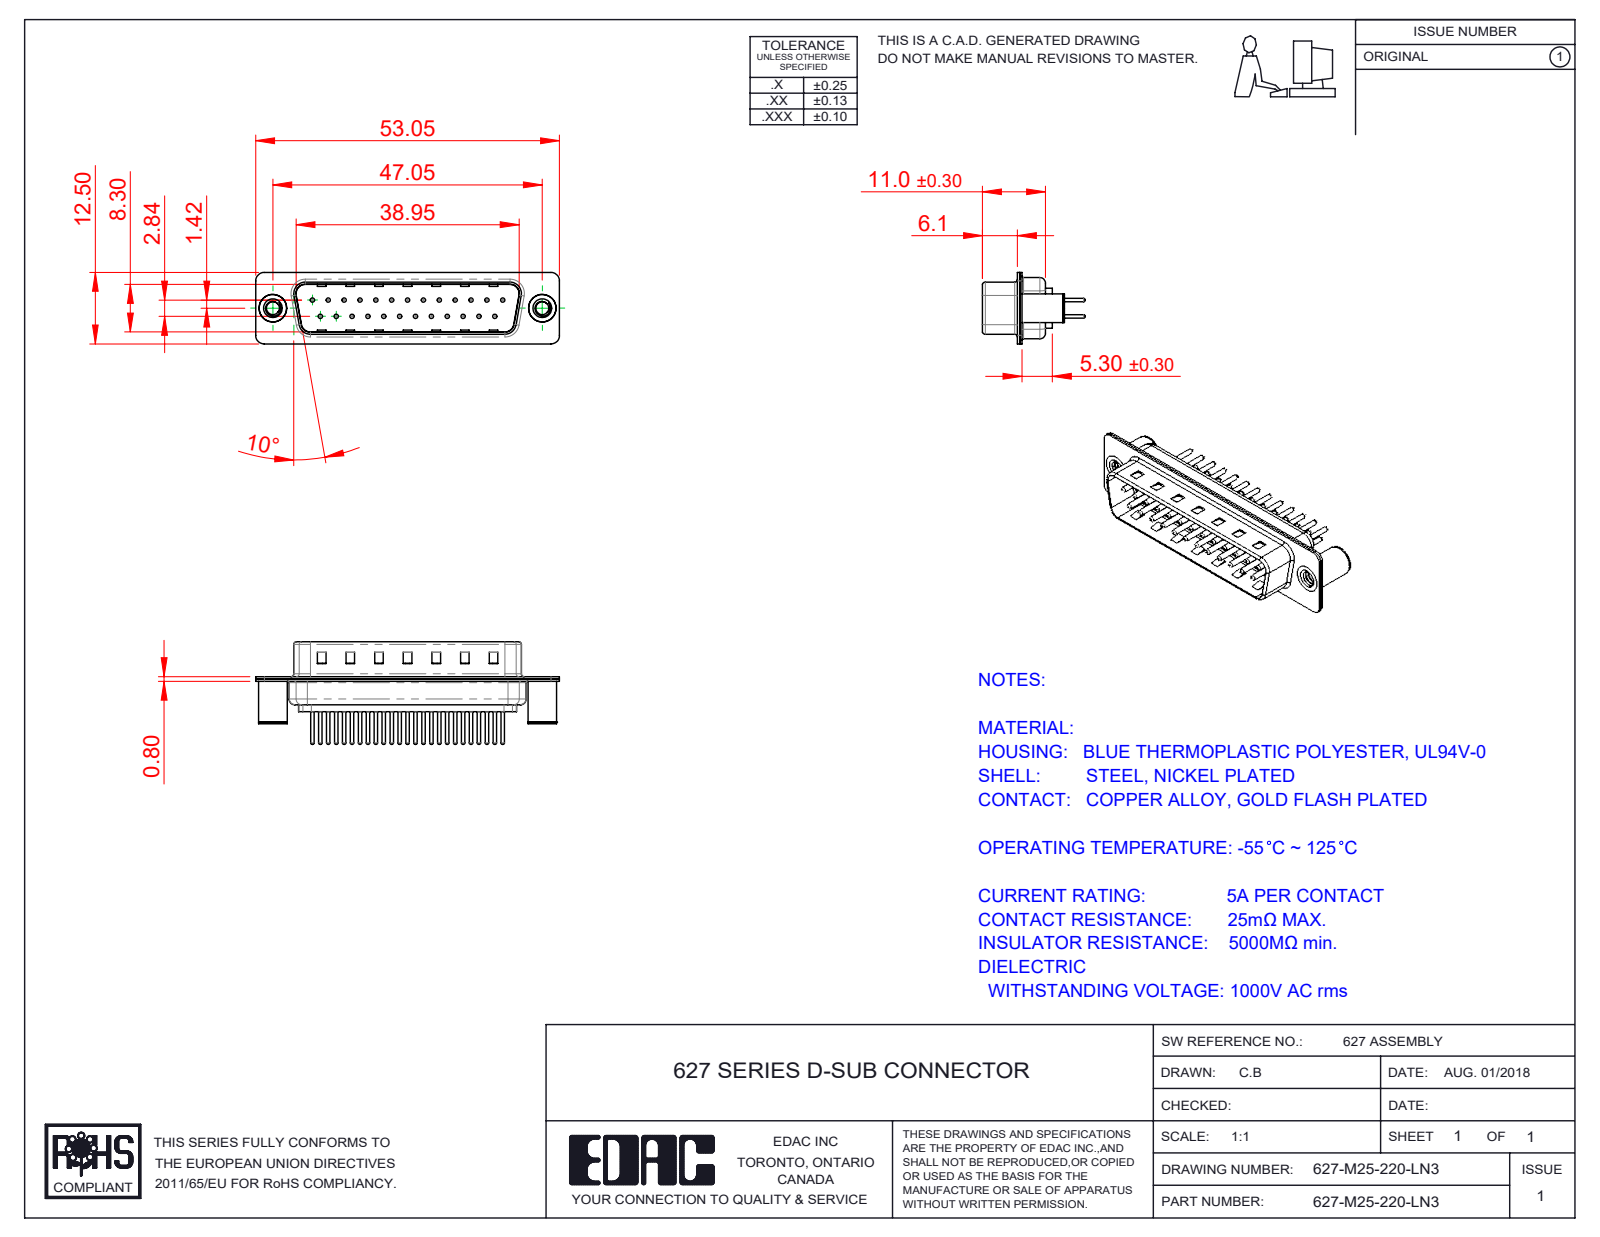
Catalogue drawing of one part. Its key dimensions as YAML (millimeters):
part_name: "627M 4-40 Threaded Board Spacer; 627M Shell Rear_25 Contacts; 627M Contact Row 2_20; 627M Shell Front_25 Contacts (+3 more)"
step_written_by: "SolidWorks 2020 (CONFIG_CONTROL_DESIGN)"
units: millimeters
bodies: {solids: 30, faces: 1335, planar: 346, cylindrical: 511, other: 478}
overall_size: [53.05, 17.9, 12.5]
volume: 2842
surface_area: 7101
round_holes:
  - {diameter: 0.75, count: 25}
  - {diameter: 1.6, count: 25}
  - {diameter: 2, count: 25}
  - {diameter: 2.26, count: 2}
  - {diameter: 3.26, count: 2}
  - {diameter: 4, count: 2}
  - {diameter: 4.8, count: 2}
round_bosses_or_shafts:
  - {diameter: 1.5, count: 25}
  - {diameter: 0.6, count: 25}
  - {diameter: 5, count: 2}
  - {diameter: 4.9, count: 2}
partial_cylinders:
  - {radius: 1.5, count: 16}
  - {radius: 2, count: 12}
  - {radius: 0.5, count: 8}
  - {radius: 1.6, count: 8}
  - {radius: 0.25, count: 4}
  - {radius: 0.6, count: 4}
  - {radius: 0.65, count: 4}
  - {radius: 0.9, count: 4}
face_to_face_distances: [0.4, 0.8, 9.5, 9.1, 8.7, 9.9, 1.2, 6.1, 5.7, 0.75]
hole_center_spacings: [3.16, 2.77, 5.54, 8.31, 11.08, 13.85, 16.62, 5.03]
